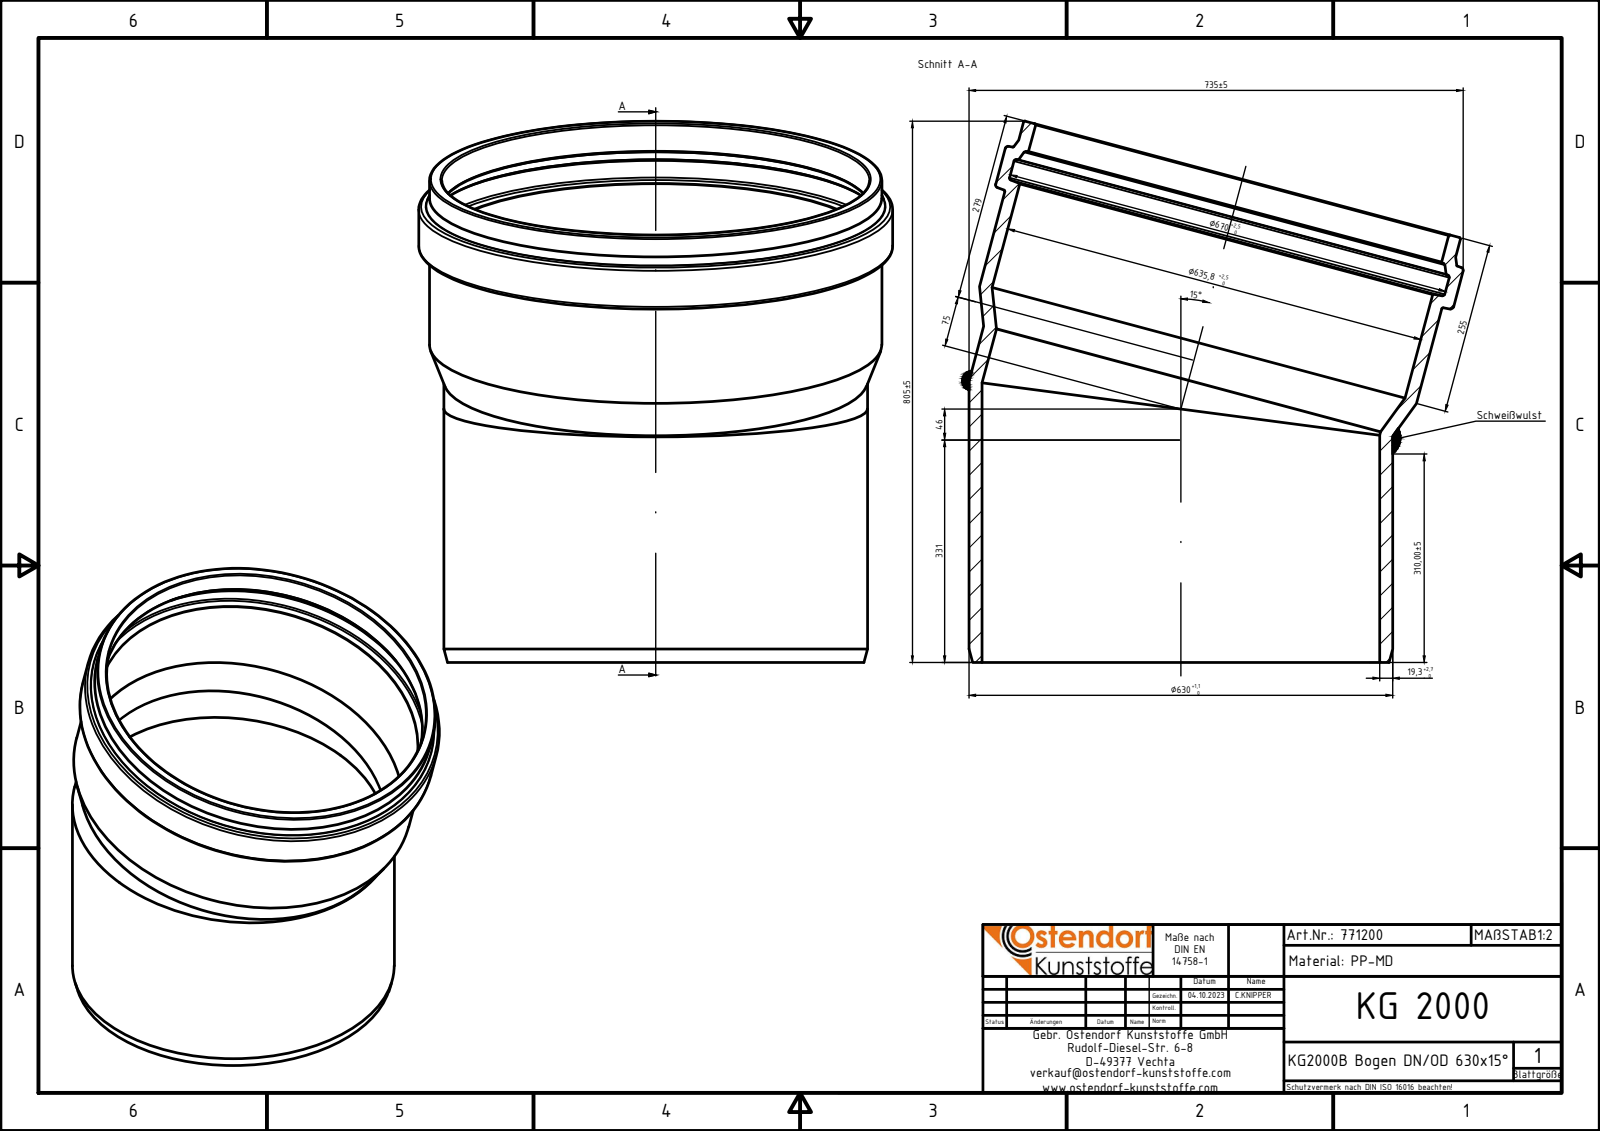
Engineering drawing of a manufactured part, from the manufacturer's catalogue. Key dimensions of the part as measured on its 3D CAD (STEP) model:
Part name (STEP PRODUCT): KGB DN630x15° KG2000 - Zusammenbau; KGB DN630x15° KG2000 - Teil 1; KGB DN630x15° KG2000 - Teil 2
STEP written by: Autodesk Inventor 2021 (AUTOMOTIVE_DESIGN)
Units: millimetres
Bodies: 2 solids, 38 faces (4 planar, 10 cylindrical, 24 other)
Overall size (bounding box): 785 × 736.96 × 703
Volume: 27 460 000 mm³ · Surface area: 3 058 000 mm²
Round holes (diameter × count): ⌀590.2 ×2, ⌀634.5 ×1, ⌀636.5 ×1, ⌀668 ×1
Round bosses / shafts (diameter × count): ⌀630 ×2, ⌀703 ×1, ⌀671.3 ×1, ⌀669.3 ×1
